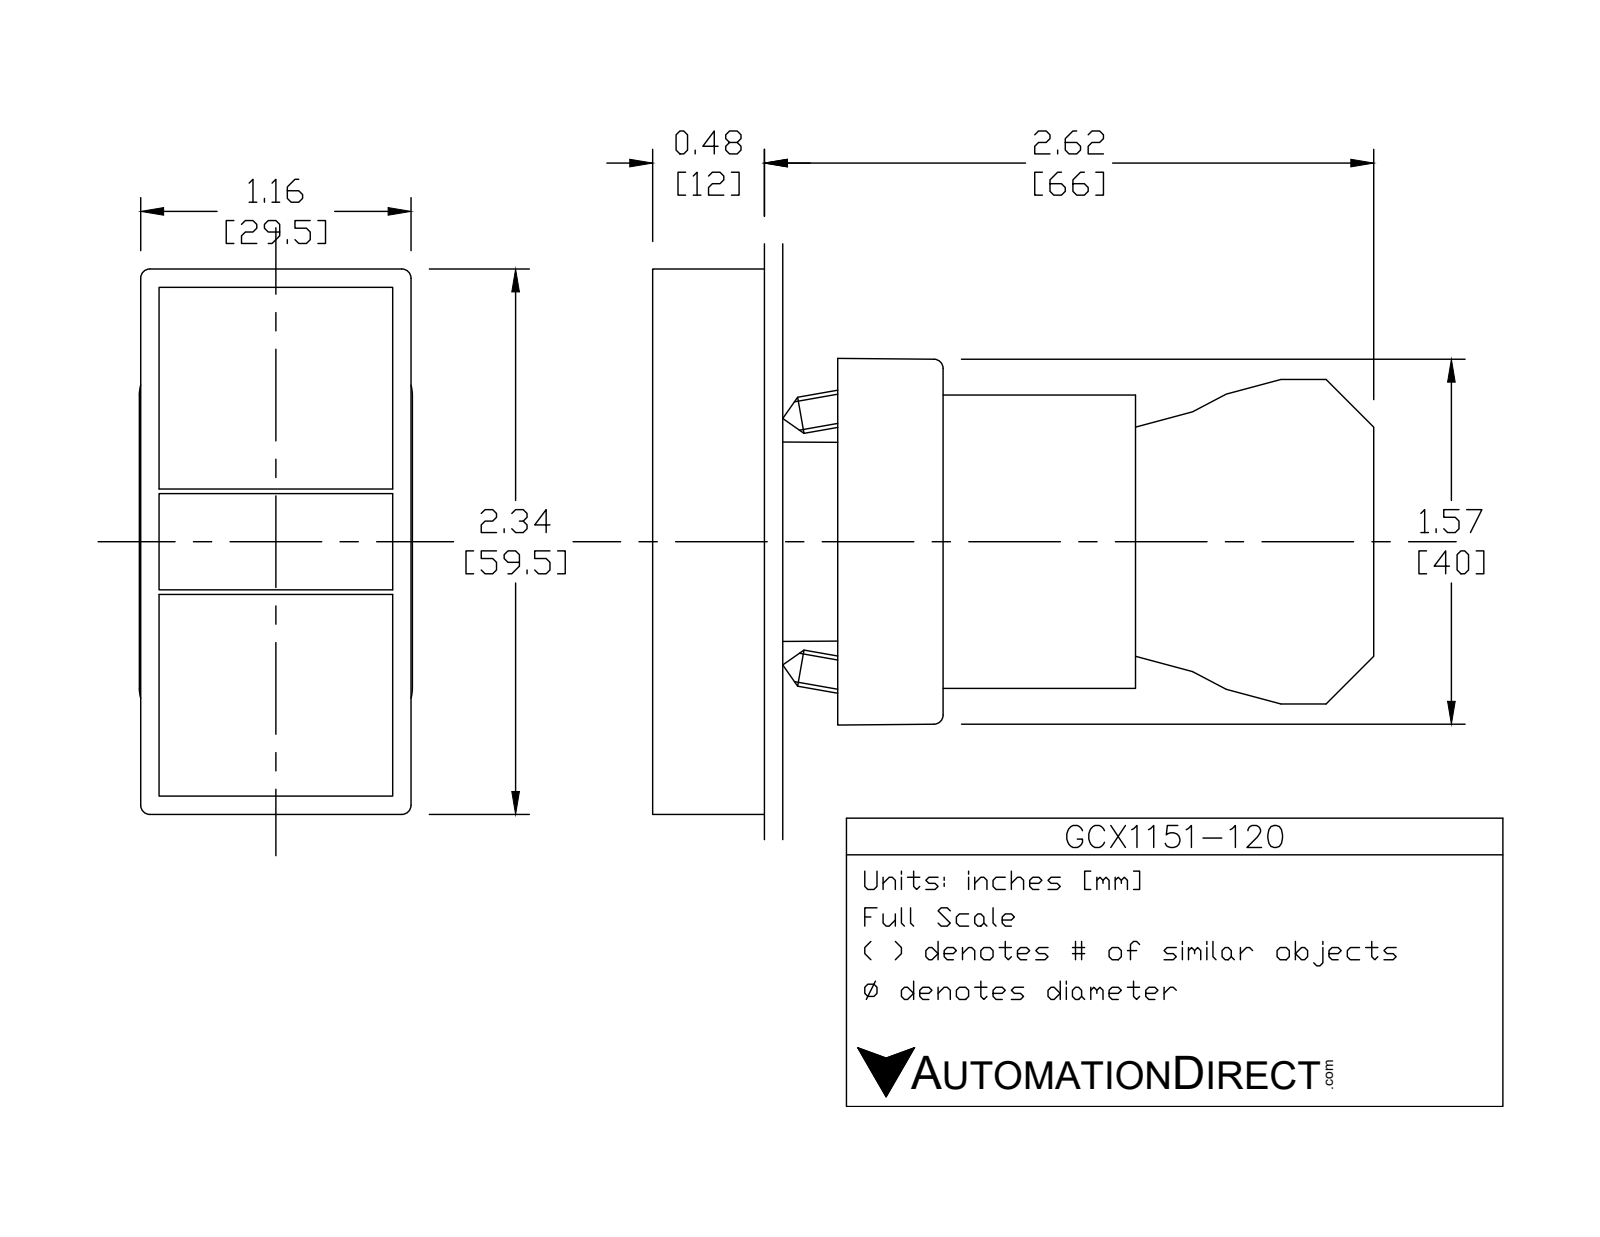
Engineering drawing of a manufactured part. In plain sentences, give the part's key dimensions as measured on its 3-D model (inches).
The part is named "ecx1030; ecx1040; GCX1151-120; GCX1151-24 OPERATOR (+2 more)". Its 3-D file was written by "SolidWorks 2016 (AUTOMOTIVE_DESIGN)". It is 9 solids with 531 faces: 348 planar, 152 cylindrical and 31 other. Overall it measures 3.043 by 2.343 by 1.177 inches. Its volume is 4.281 cubic inches and its surface area 55.77 square inches. Round holes: 4 of diameter 0.079, 2 of diameter 0.087, 2 of diameter 0.124, 2 of diameter 0.13, 1 of diameter 0.197, 1 of diameter 0.469, 1 of diameter 0.878, 1 of diameter 0.888. Round bosses or shafts: 4 of diameter 0.157, 1 of diameter 0.945, 1 of diameter 0.856, 1 of diameter 0.78, 1 of diameter 0.504. Partial cylindrical surfaces (rounded edges, fillets, slot ends): 24 of radius 0.059, 12 of radius 0.041, 12 of radius 0.124, 12 of radius 0.157, 8 of radius 0.039, 2 of radius 0.063, 2 of radius 0.079, 2 of radius 0.128. The main face-to-face distances are 0.039, 0.059, 0.02, 0.453, 0.579, 0.593, 0.74, 1.193, 0.827, 1.567. The hole center spacings are 0.236, 1.003, 0.974, 0.472, 0.539, 0.544, 1.083, 0.484.
